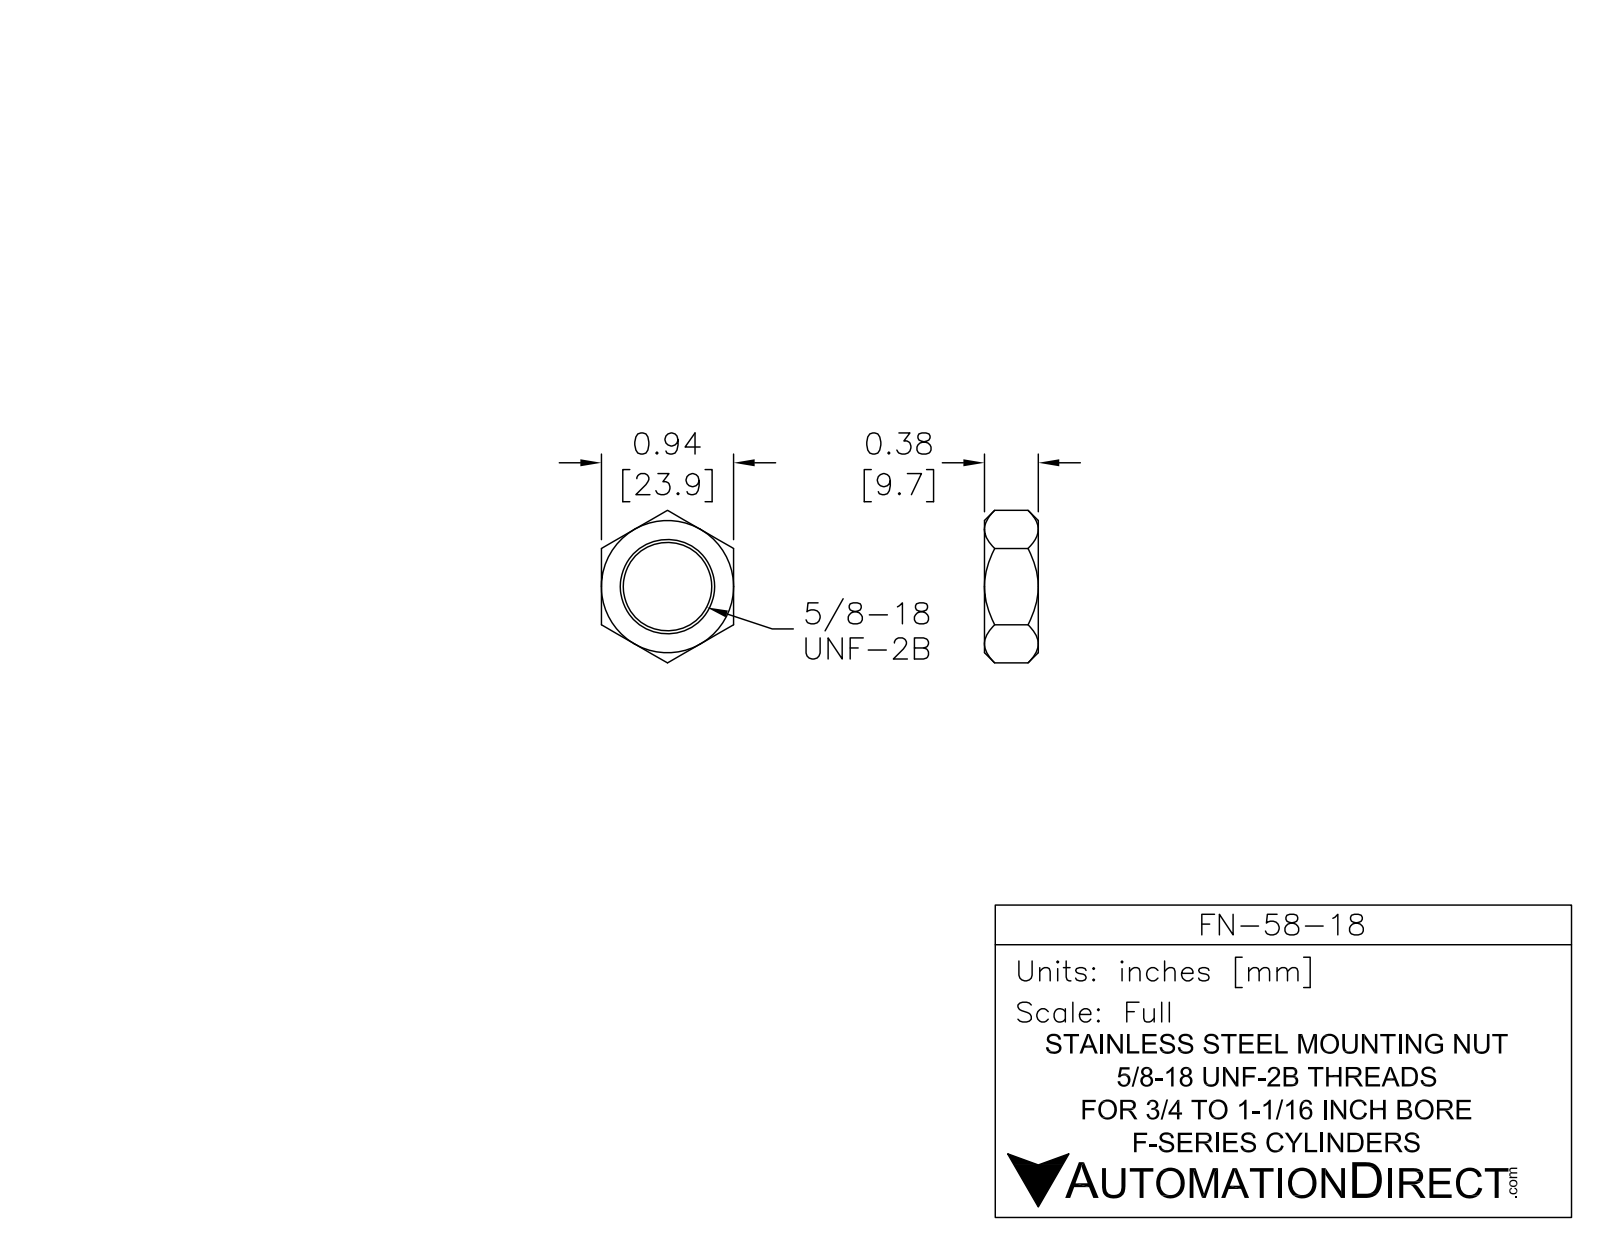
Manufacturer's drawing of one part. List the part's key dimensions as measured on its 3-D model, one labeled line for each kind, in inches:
Part name (STEP PRODUCT): FN-58-18
STEP written by: SolidWorks 2017 (AUTOMOTIVE_DESIGN)
Units: inches
Bodies: 1 solid, 24 faces (8 planar, 2 cylindrical, 14 other)
Overall size (bounding box): 1.083 × 0.938 × 0.375
Volume: 0.184 in³ · Surface area: 2.798 in²
Round holes (diameter × count): ⌀0.578 ×1
Main face-to-face distances: 0.938, 0.375
